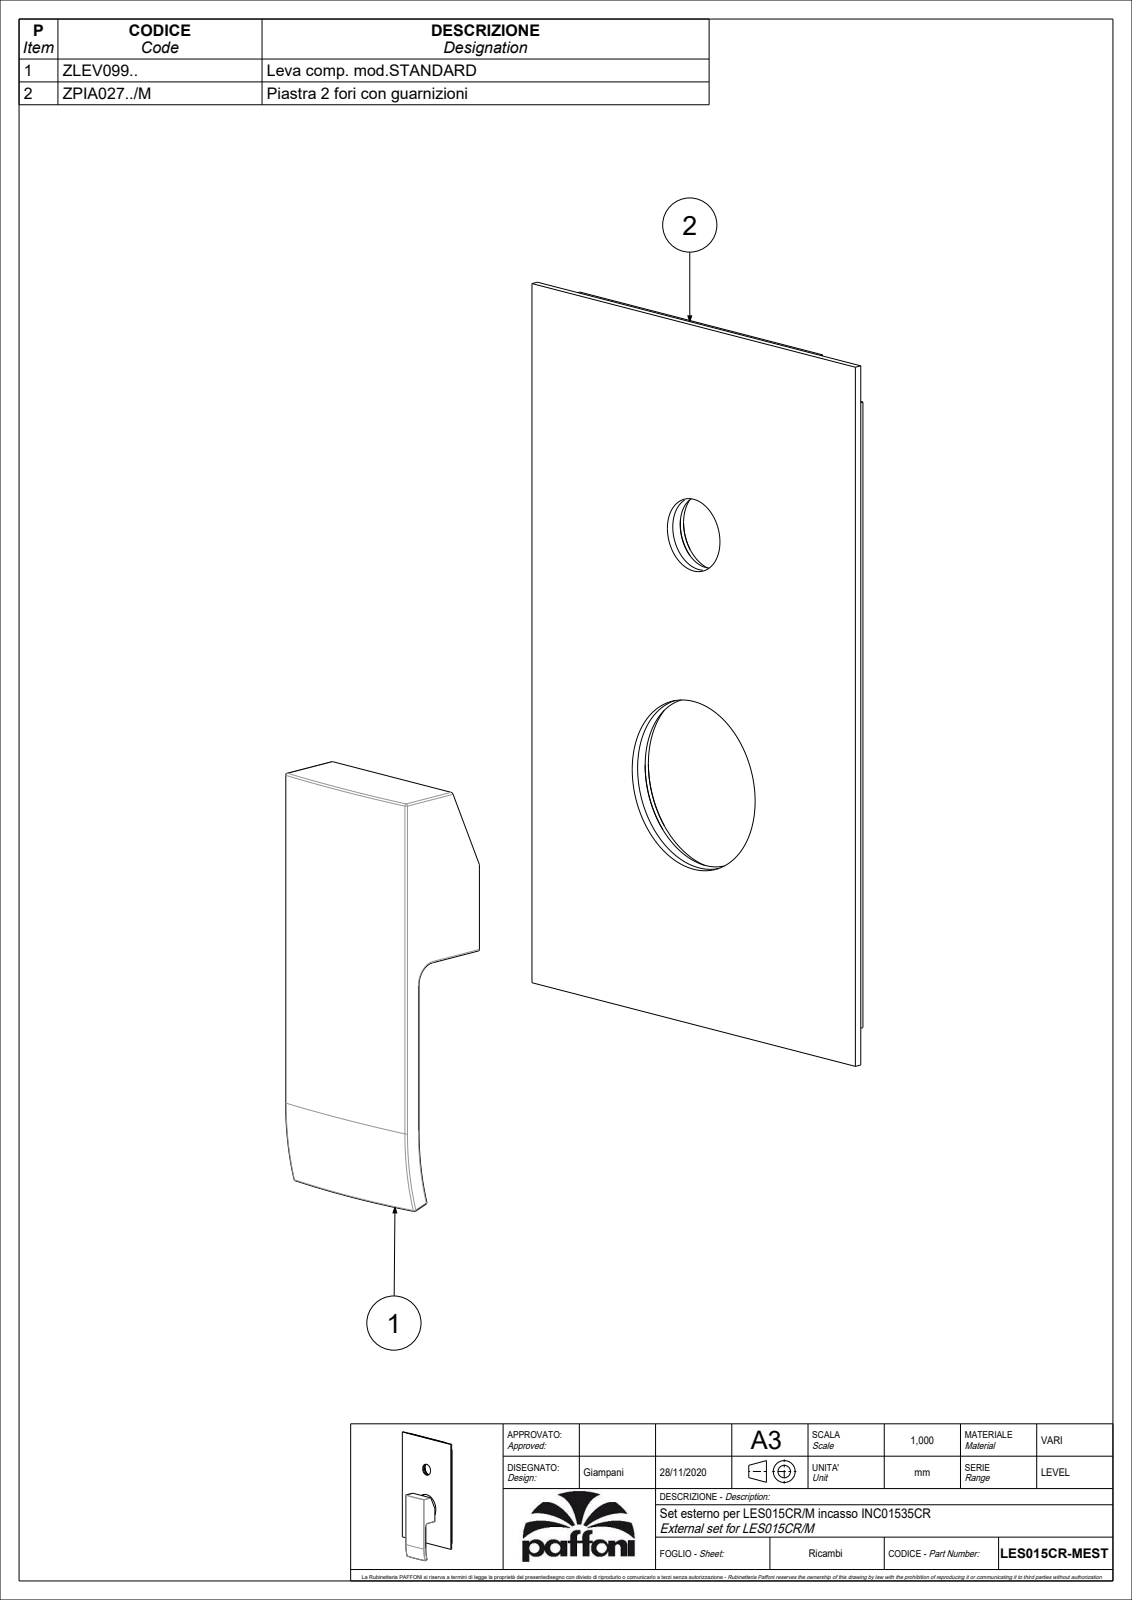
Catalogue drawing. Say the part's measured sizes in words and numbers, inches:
The part is named "LES015CR-MEST". Its 3-D file was written by "CREO PARAMETRIC BY PTC INC, 2020044 (CONFIG_CONTROL_DESIGN)". It is 2 solids with 200 faces: 80 planar, 71 cylindrical and 49 other. Overall it measures 8.361 by 4.724 by 1.476 inches. Its volume is 5.058 cubic inches and its surface area 106.2 square inches. Round holes: 1 of diameter 0.118, 1 of diameter 0.13, 1 of diameter 0.217, 1 of diameter 0.307, 1 of diameter 0.768, 1 of diameter 0.846, 1 of diameter 0.984, 1 of diameter 1.795, 1 of diameter 1.874, 1 of diameter 2.012. Round bosses or shafts: 1 of diameter 2.15, 1 of diameter 1.122, 1 of diameter 0.299, 1 of diameter 0.197. Partial cylindrical surfaces (rounded edges, fillets, slot ends): 14 of radius 0.059, 10 of radius 0.02, 4 of radius 0.079, 2 of radius 11.811, 1 of radius 0.089. The main face-to-face distances are 0.079, 0.031, 0.11, 1.772, 1.181, 1.15, 1.071, 1.476, 3.248, 0.217. The hole center spacings are 2.677.
